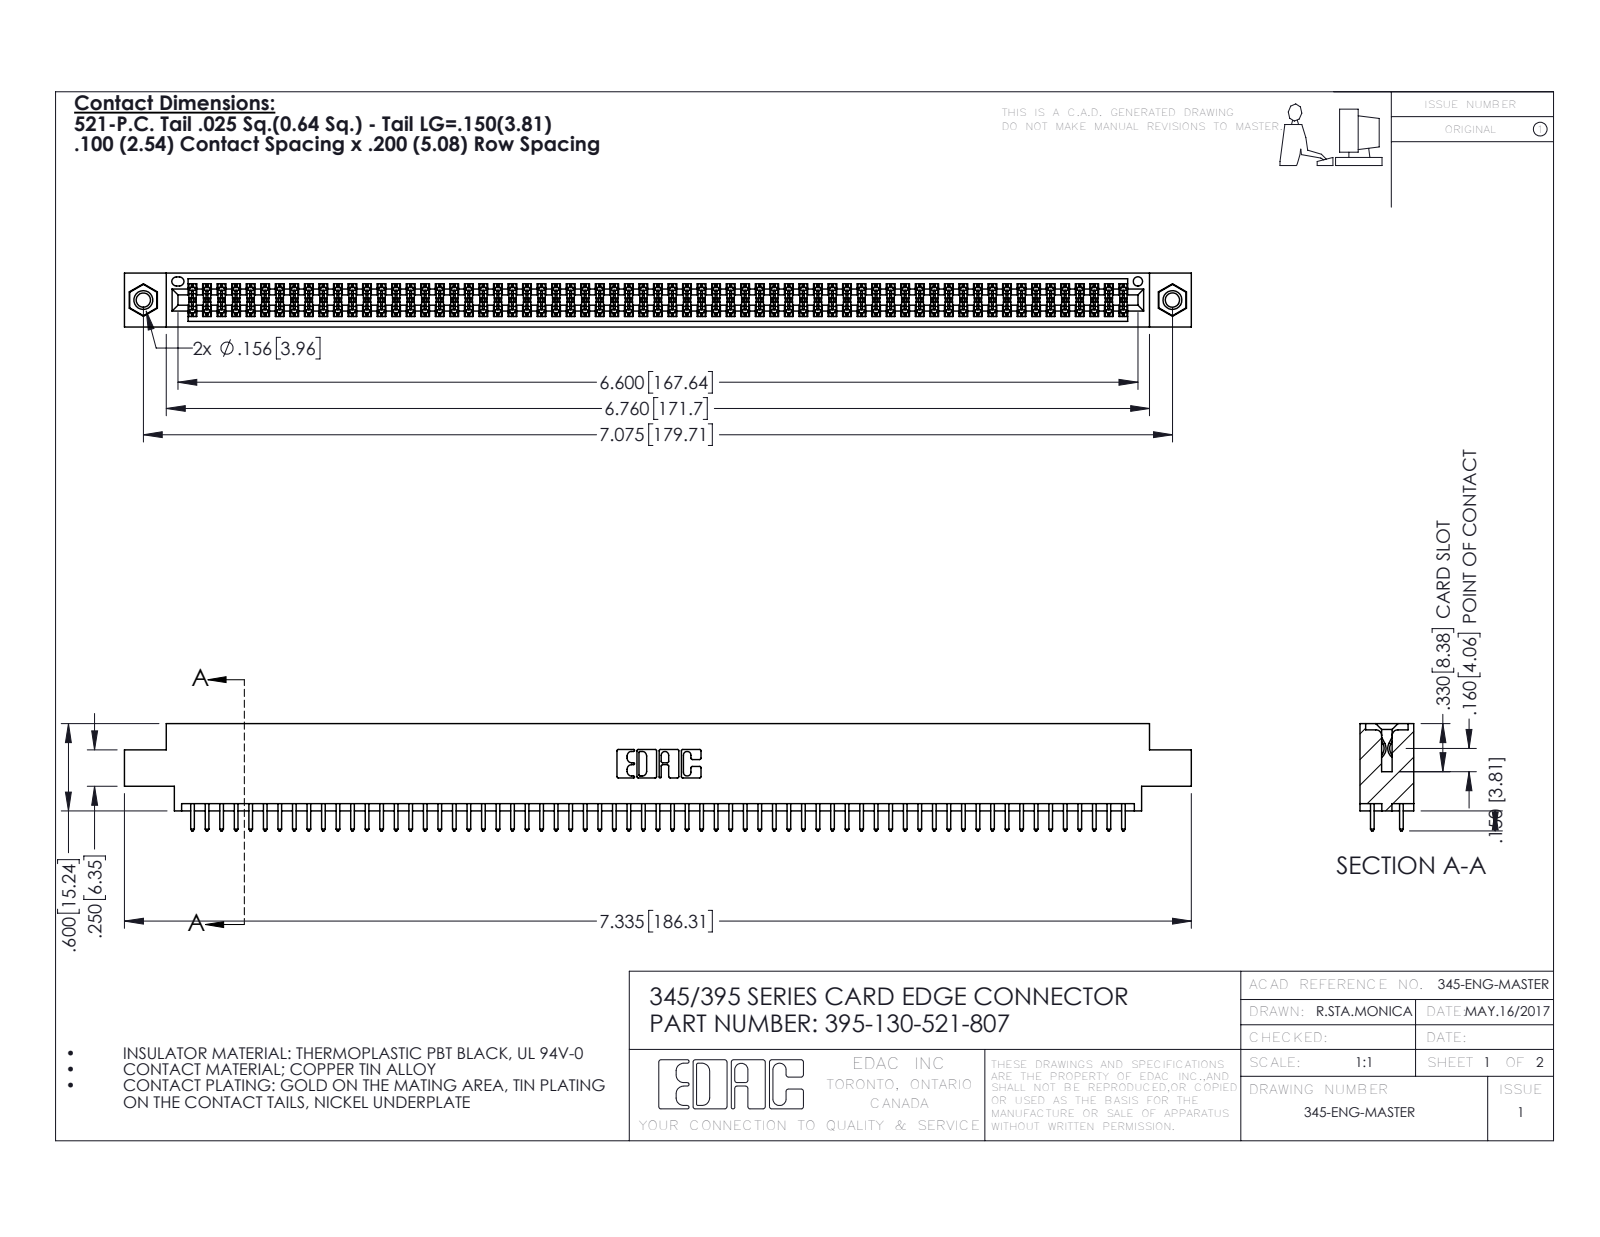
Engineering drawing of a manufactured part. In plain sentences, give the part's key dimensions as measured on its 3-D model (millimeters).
The part is named "345-292-001_345-293-121; 395-130-521-807; 345-250-001_345-250-005-103; 345 Part_0.170 Offset - 0.156 Dia-TI". Its 3-D file was written by "SolidWorks 2016 (CONFIG_CONTROL_DESIGN)". It is 133 solids with 6690 faces: 4406 planar, 2268 cylindrical and 16 other. Overall it measures 186.3 by 18.7 by 9.4 millimeters. Its volume is 18 120 cubic millimeters and its surface area 27 070 square millimeters. Round holes: 2 of diameter 2.5, 2 of diameter 3.2, 2 of diameter 4, 1 of diameter 1.6. Round bosses or shafts: 2 of diameter 3.9. Partial cylindrical surfaces (rounded edges, fillets, slot ends): 195 of radius 0.2, 130 of radius 0.3, 22 of radius 0.3, 6 of radius 0.2, 6 of radius 0.8, 3 of radius 0.7, 2 of radius 0.4, 2 of radius 0.5. The main face-to-face distances are 1.8, 7.6, 5.1, 9.4, 2.5, 6.9, 0.6, 5.7, 4.4, 3.8. The hole center spacings are 6.9, 173.7, 179.7.
